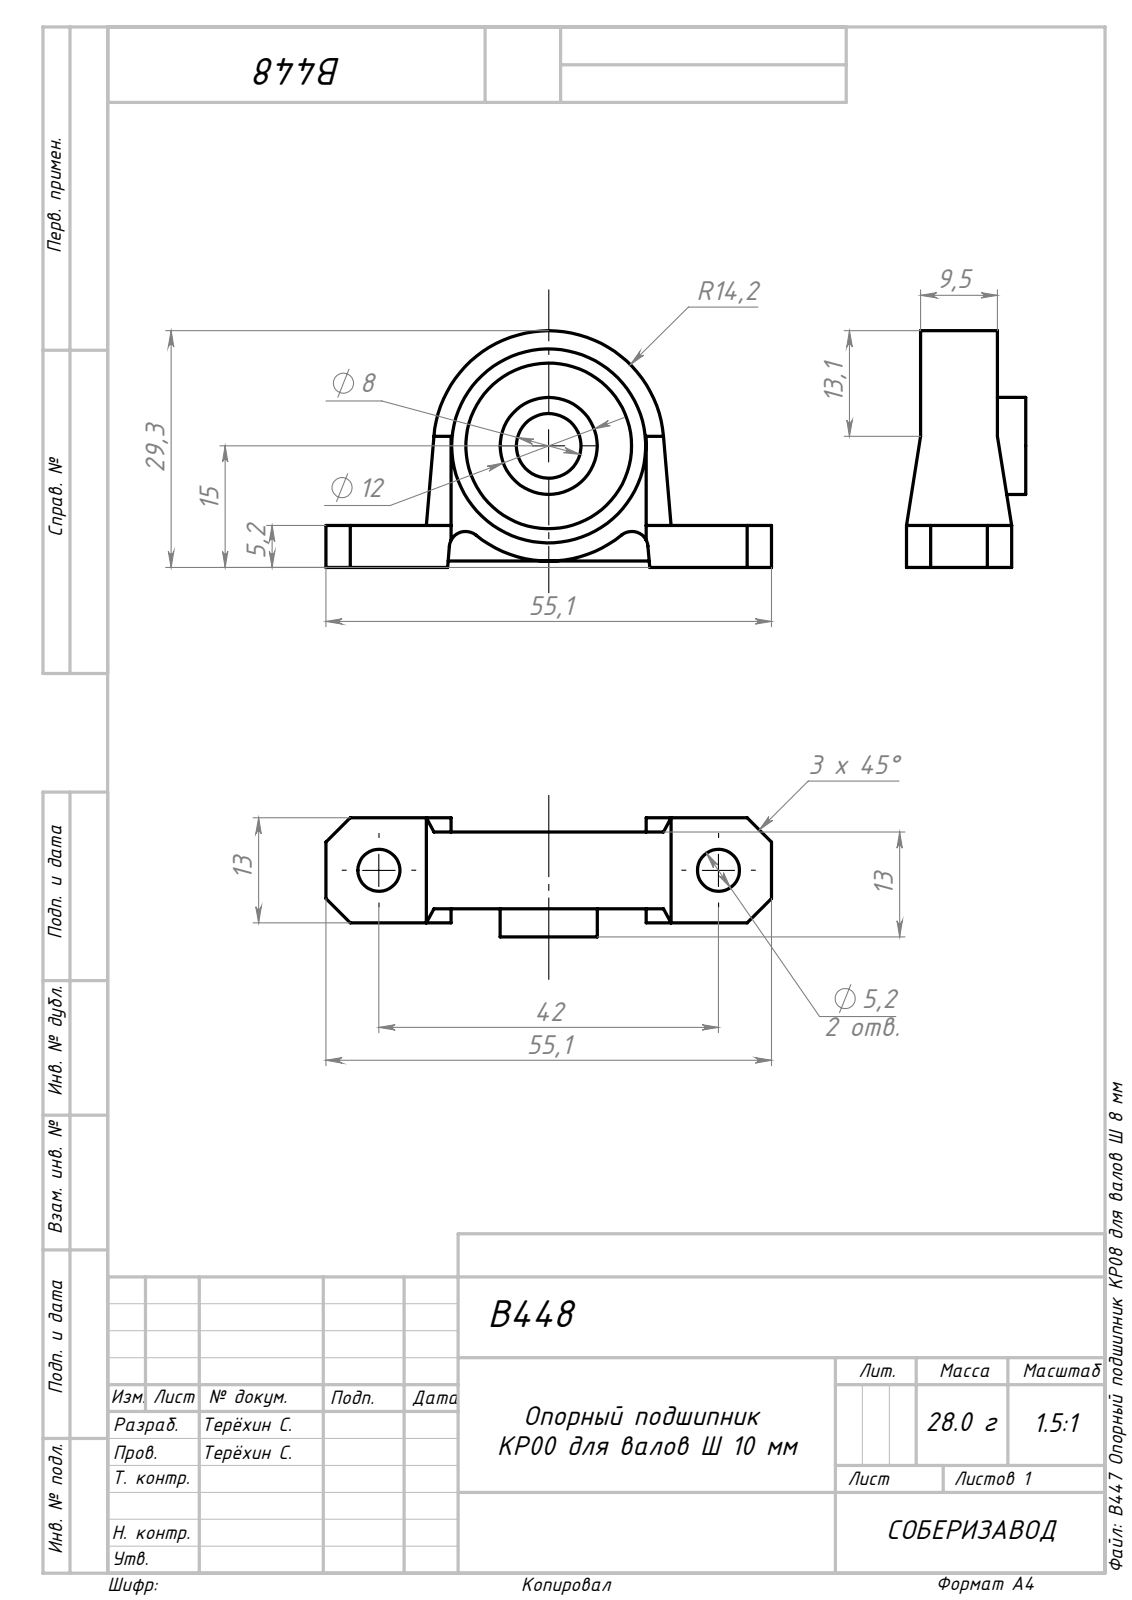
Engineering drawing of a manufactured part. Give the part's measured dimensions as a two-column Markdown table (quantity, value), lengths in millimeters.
| quantity | value |
| --- | --- |
| part name | B447 Опорный подшипник KP08 для валов Ø 8 мм_00; Сборка1 |
| STEP written by | SolidWorks 2024 (AUTOMOTIVE_DESIGN) |
| units | millimeters |
| bodies | 3 solids, 64 faces (39 planar, 25 cylindrical, 0 other) |
| overall size | 55.1 × 29.3 × 14.75 |
| volume | 6 702 mm³ |
| surface area | 5 435 mm² |
| round holes (diameter × count) | 5.2 × 2, 8 × 1, 12 × 1, 20.5 × 1, 24 × 1 |
| partial cylindrical surfaces (radius × count) | 2 × 2, 14.25 × 1 |
| main face-to-face distances | 2, 7.5, 5.5, 1.75, 5.2, 3.75, 9.25, 11.25, 4, 9 |
| hole center spacings | 42 |
